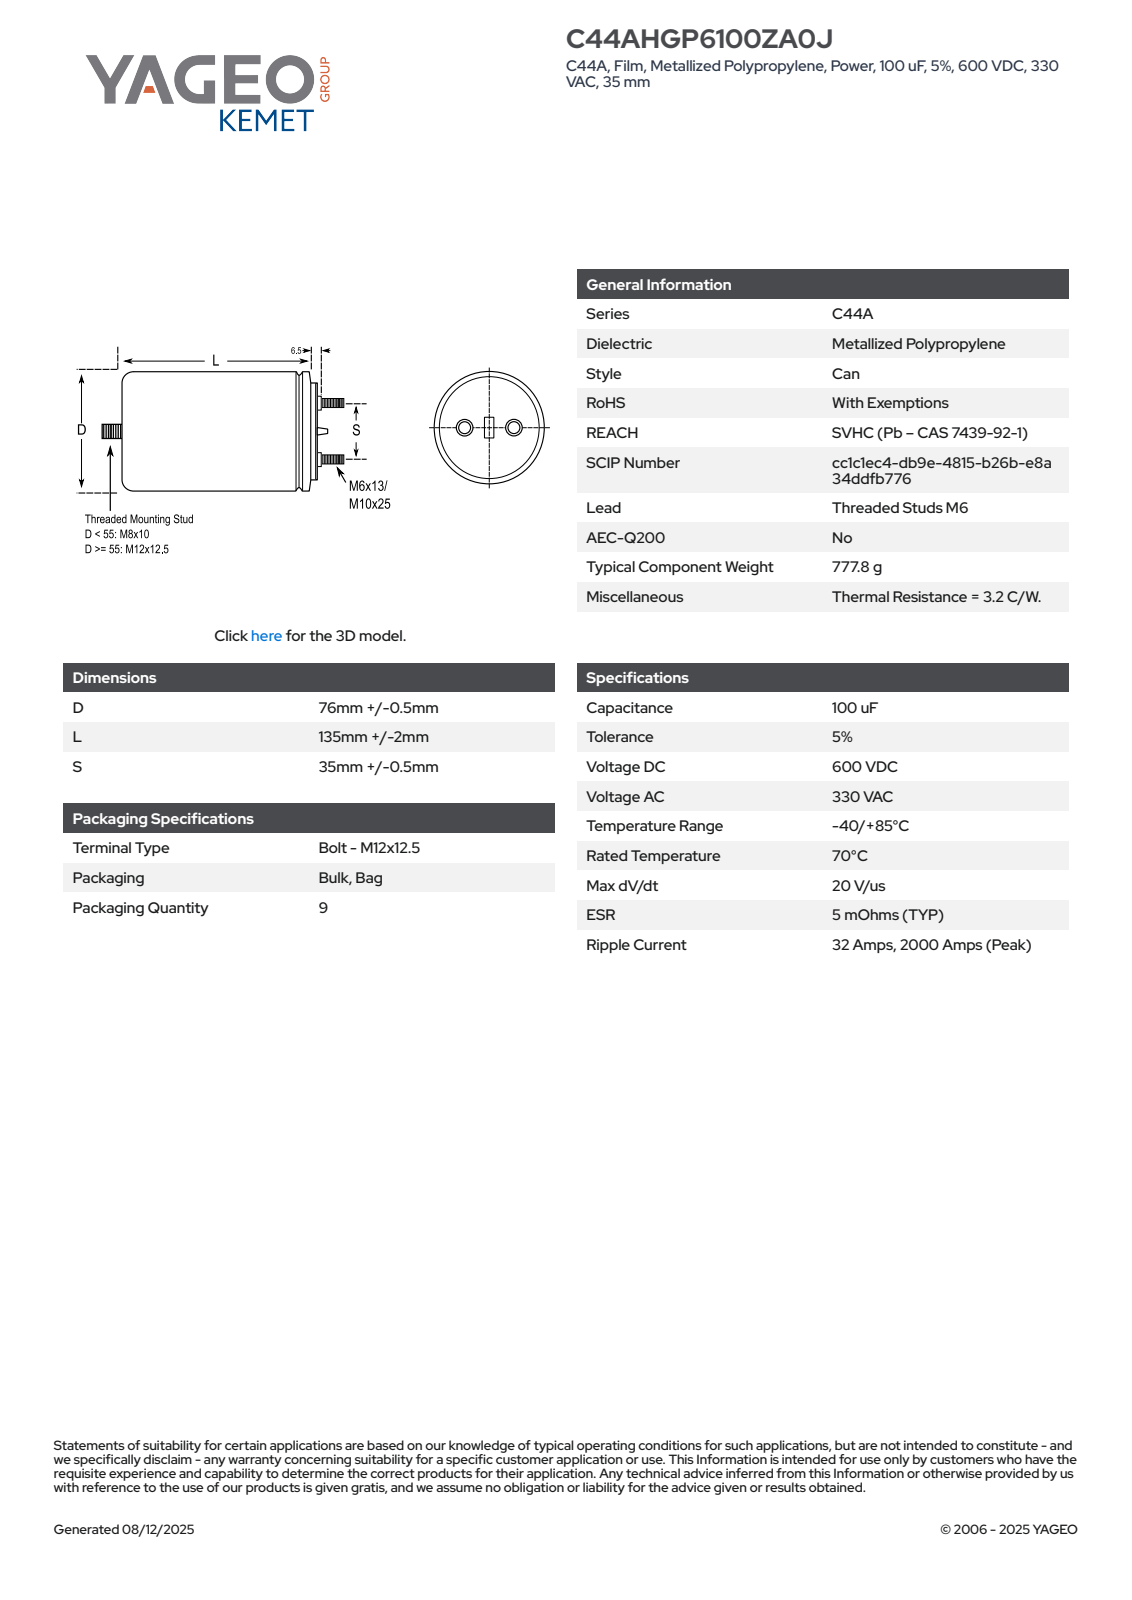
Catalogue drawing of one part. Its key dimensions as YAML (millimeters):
part_name: "CFP_C44A_76X135_D76.5L137S35"
step_written_by: "SolidWorks 2014 (AUTOMOTIVE_DESIGN)"
units: millimeters
bodies: {solids: 1, faces: 102, planar: 29, cylindrical: 34, other: 39}
overall_size: [169, 76.5, 76.5]
volume: 641297
surface_area: 43779
round_bosses_or_shafts:
  - {diameter: 9, count: 2}
  - {diameter: 6, count: 2}
  - {diameter: 76.5, count: 1}
  - {diameter: 60, count: 1}
  - {diameter: 12, count: 1}
partial_cylinders:
  - {radius: 38.24, count: 1}
face_to_face_distances: [142, 12.5, 154.5, 156, 143.5, 1.5, 169, 156.5, 14.5, 13]
